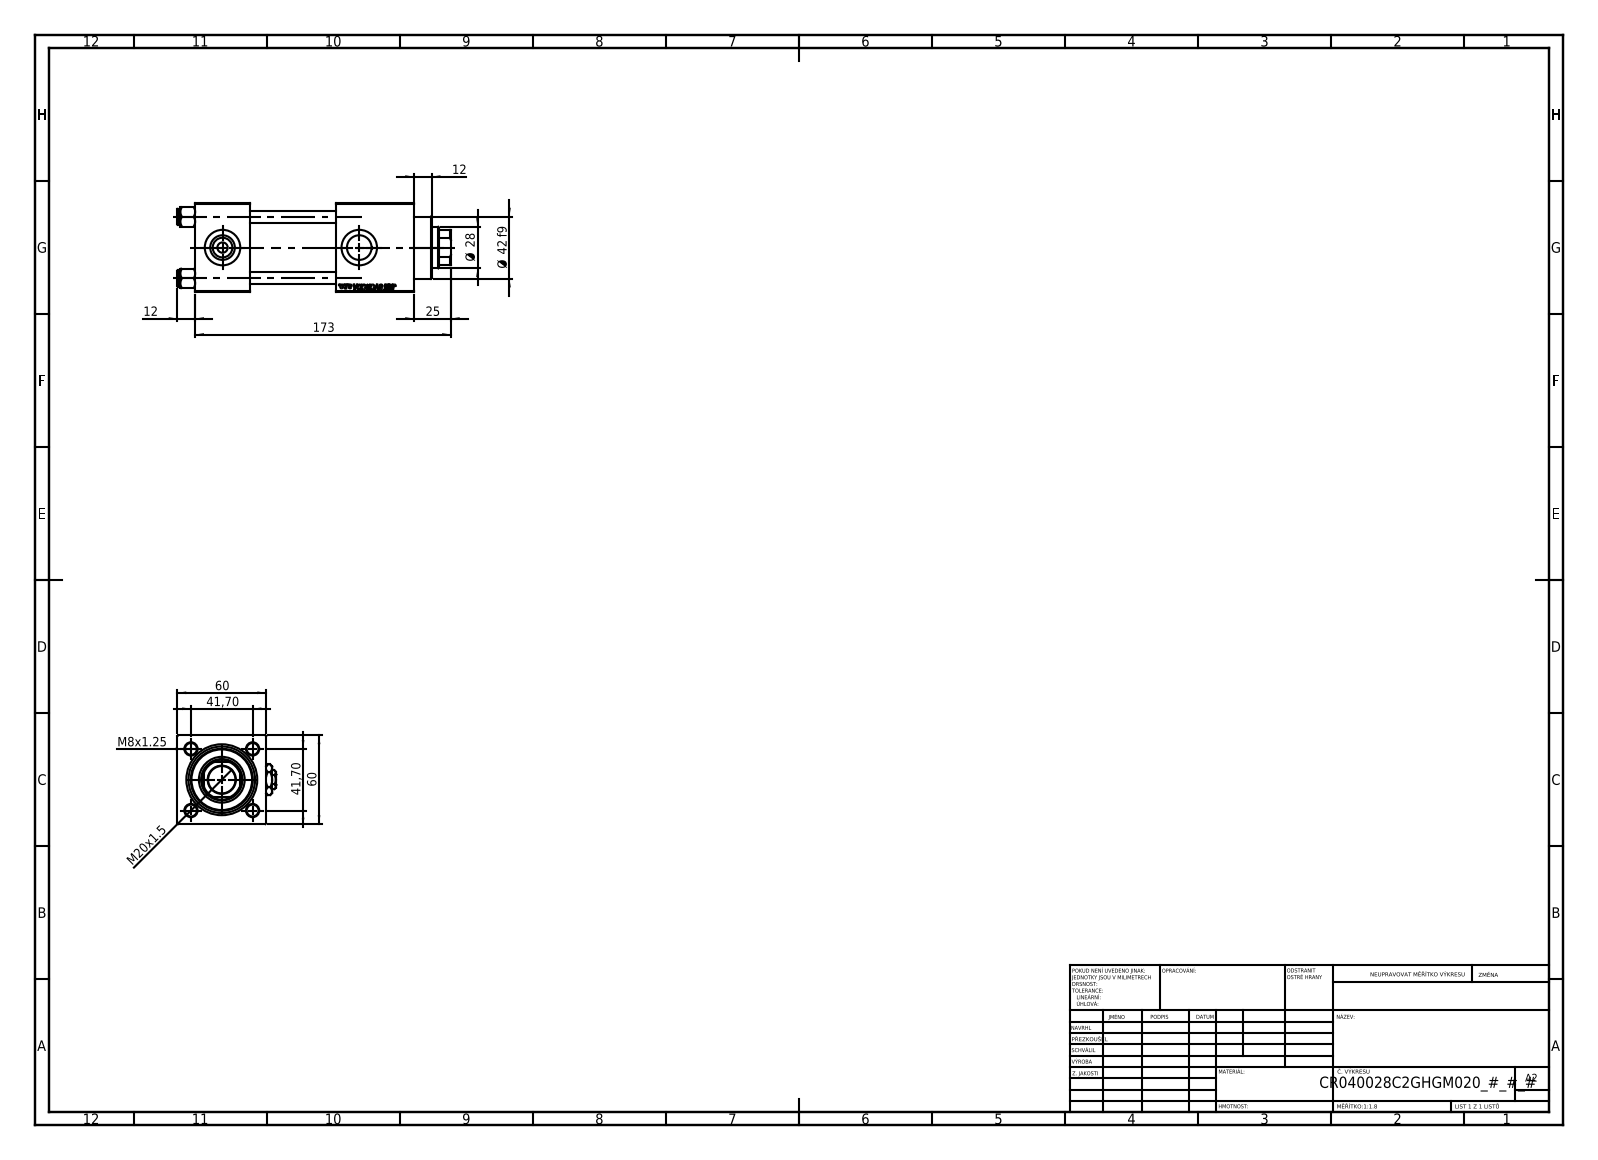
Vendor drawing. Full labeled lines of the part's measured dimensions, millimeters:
Part name (STEP PRODUCT): NUT_M5_C; V215CR_C_TYCINKA; V215_VC_A; V215CR_C_Body (+2 more)
STEP written by: SolidWorks 2019 (CONFIG_CONTROL_DESIGN)
Units: millimetres
Bodies: 12 solids, 1202 faces (550 planar, 94 cylindrical, 558 other)
Overall size (bounding box): 185 × 67 × 60
Volume: 422 827 mm³ · Surface area: 113 084 mm²
Round holes (diameter × count): ⌀8 ×4, ⌀7 ×2, ⌀16.66 ×2, ⌀24 ×2, ⌀18.5 ×1, ⌀28 ×1, ⌀31 ×1, ⌀40 ×1, ⌀45 ×1
Round bosses / shafts (diameter × count): ⌀11 ×4, ⌀46 ×1, ⌀42 ×1
Partial cylindrical surfaces — rounded edges, fillets, slot ends (radius × count): R13.5 ×1
Main face-to-face distances: 60, 37, 58, 95, 53, 119.3, 82.3, 24.3, 148, 111
Hole centre spacings: 29.49, 41.7, 58.97, 92.5
